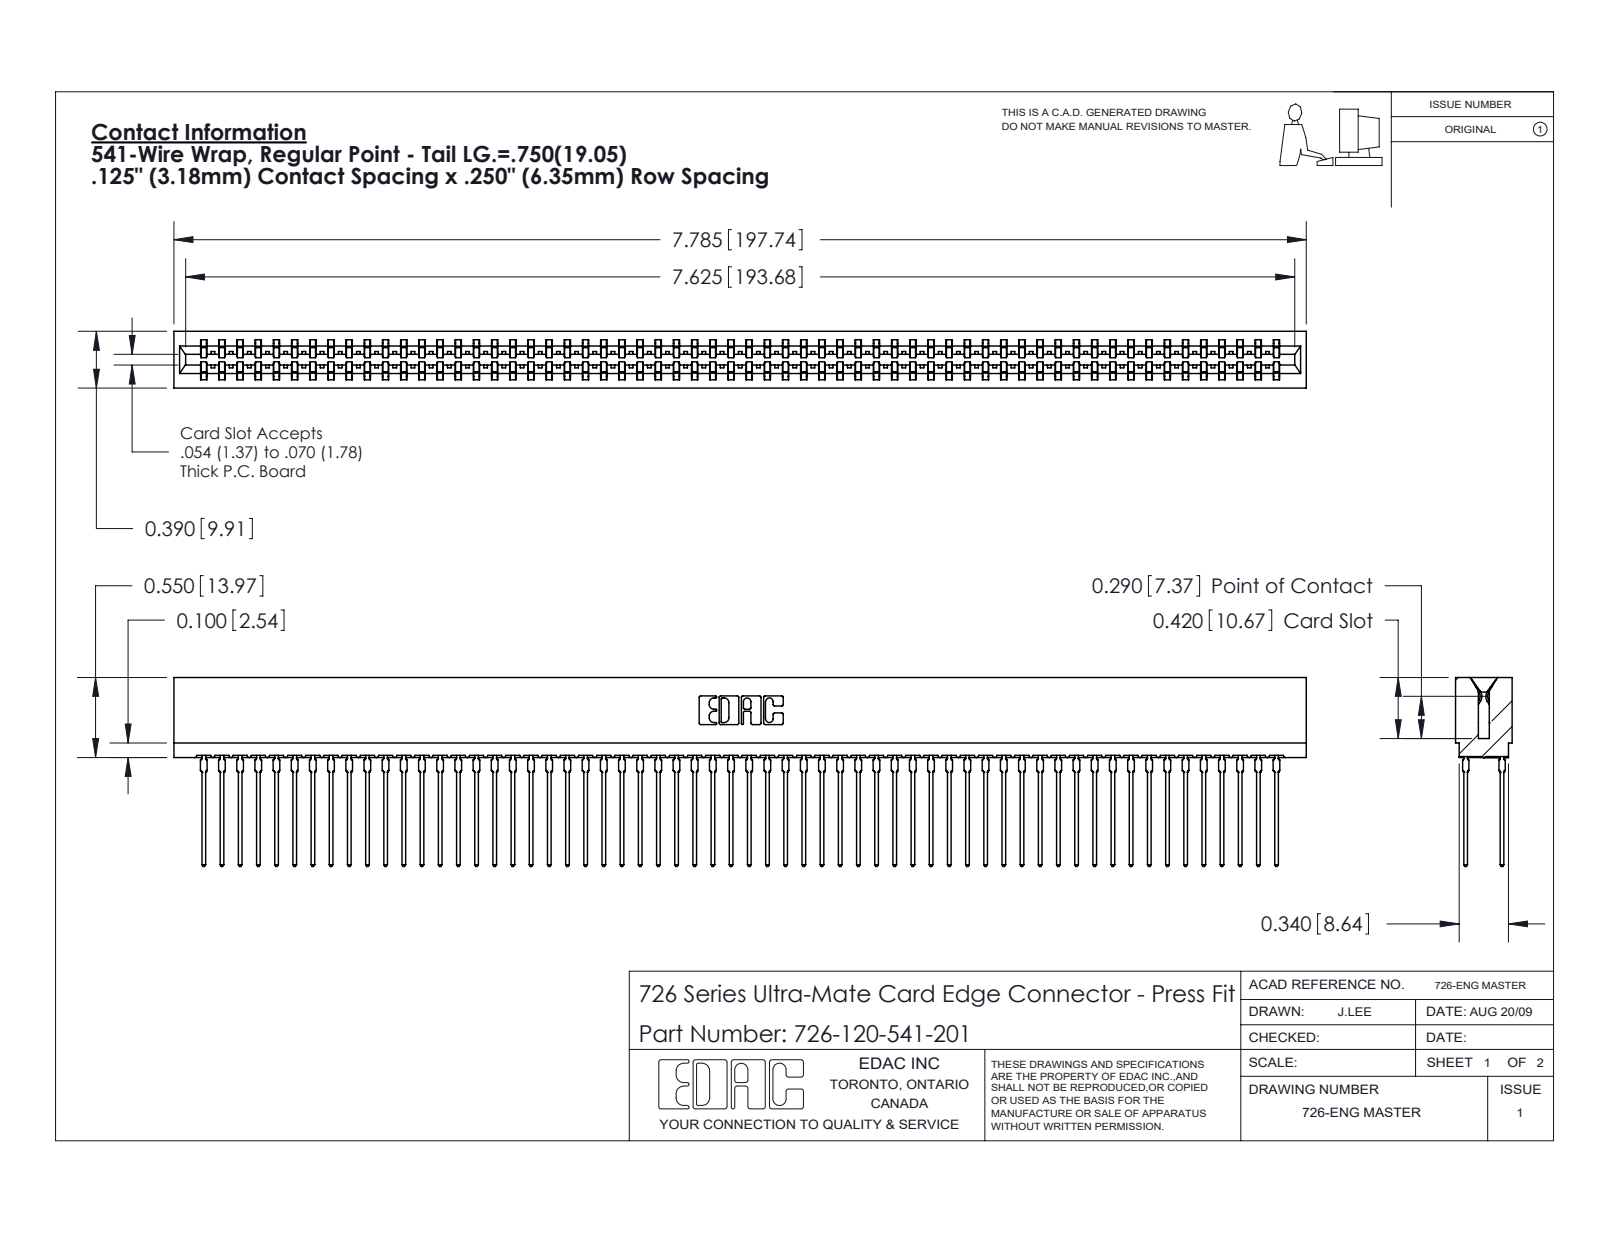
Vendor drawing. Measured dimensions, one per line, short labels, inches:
name: 746-292-001_541; 726 Part_.515 Slot Depth - 01; 726-120-541-201
written by: SolidWorks 2020 (CONFIG_CONTROL_DESIGN)
unit: in
bodies: 121 solids, 10837 faces (5575 planar, 2142 cylindrical, 3120 other)
size: 7.785 × 1.299 × 0.39
volume: 1.145 in³; area: 53.7 in²
rounds: 240× R0.021, 61× R0.015, 22× R0.01, 8× R0.005, 8× R0.011, 6× R0.007, 6× R0.031, 3× R0.026
face distances: 0.057, 0.333, 0.025, 0.307, 0.25, 0.39, 0.083, 0.275, 0.225, 0.365
